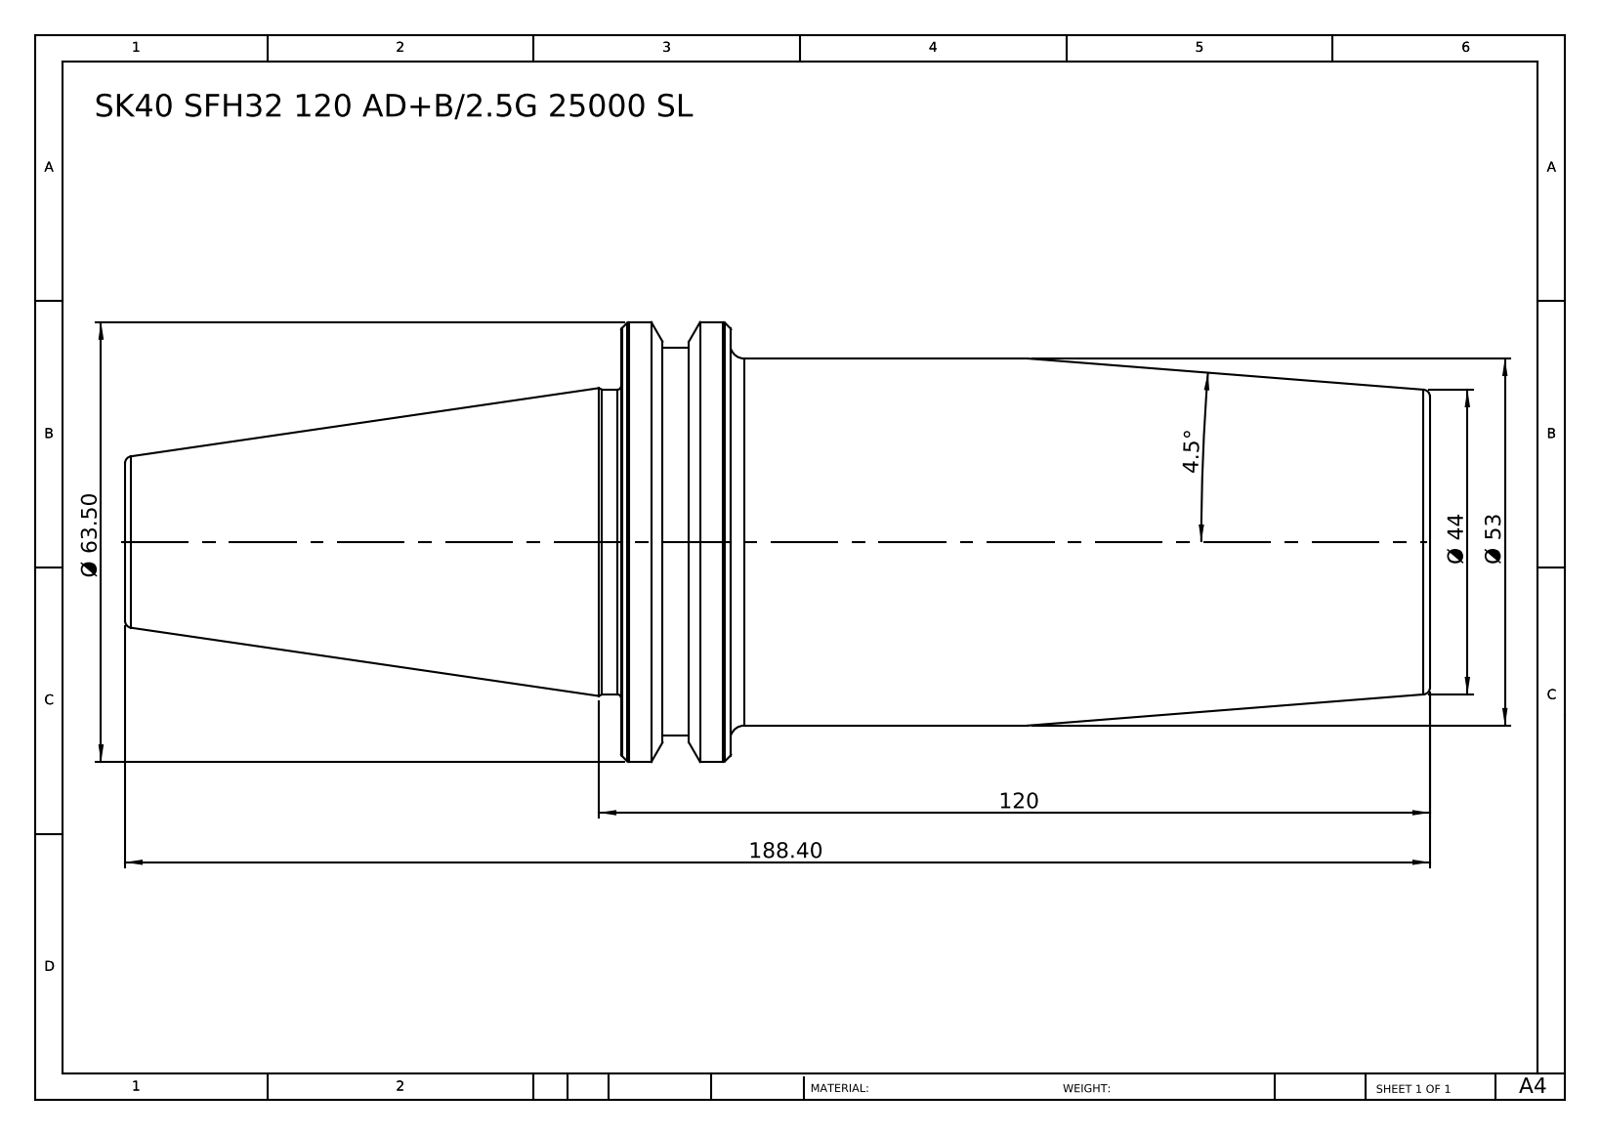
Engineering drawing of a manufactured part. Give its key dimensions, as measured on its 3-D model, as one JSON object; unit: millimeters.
{"part_name": "SK40 SFH25 120 AD+B-2.5G 25000 SL", "step_written_by": "SolidWorks 2014 (CONFIG_CONTROL_DESIGN)", "units": "millimeters", "bodies": {"solids": 1, "faces": 46, "planar": 6, "cylindrical": 10, "other": 30}, "overall_size": [188.4, 63.5, 63.5], "volume_mm3": 318946, "surface_area_mm2": 32050, "round_bosses_or_shafts": [[63.5, 1], [56, 1], [53, 1], [44, 1]], "face_to_face_distances": [116.8, 100.9, 15.9, 188.4, 87.5, 71.6, 107, 6.1, 9.8, 81.4]}
